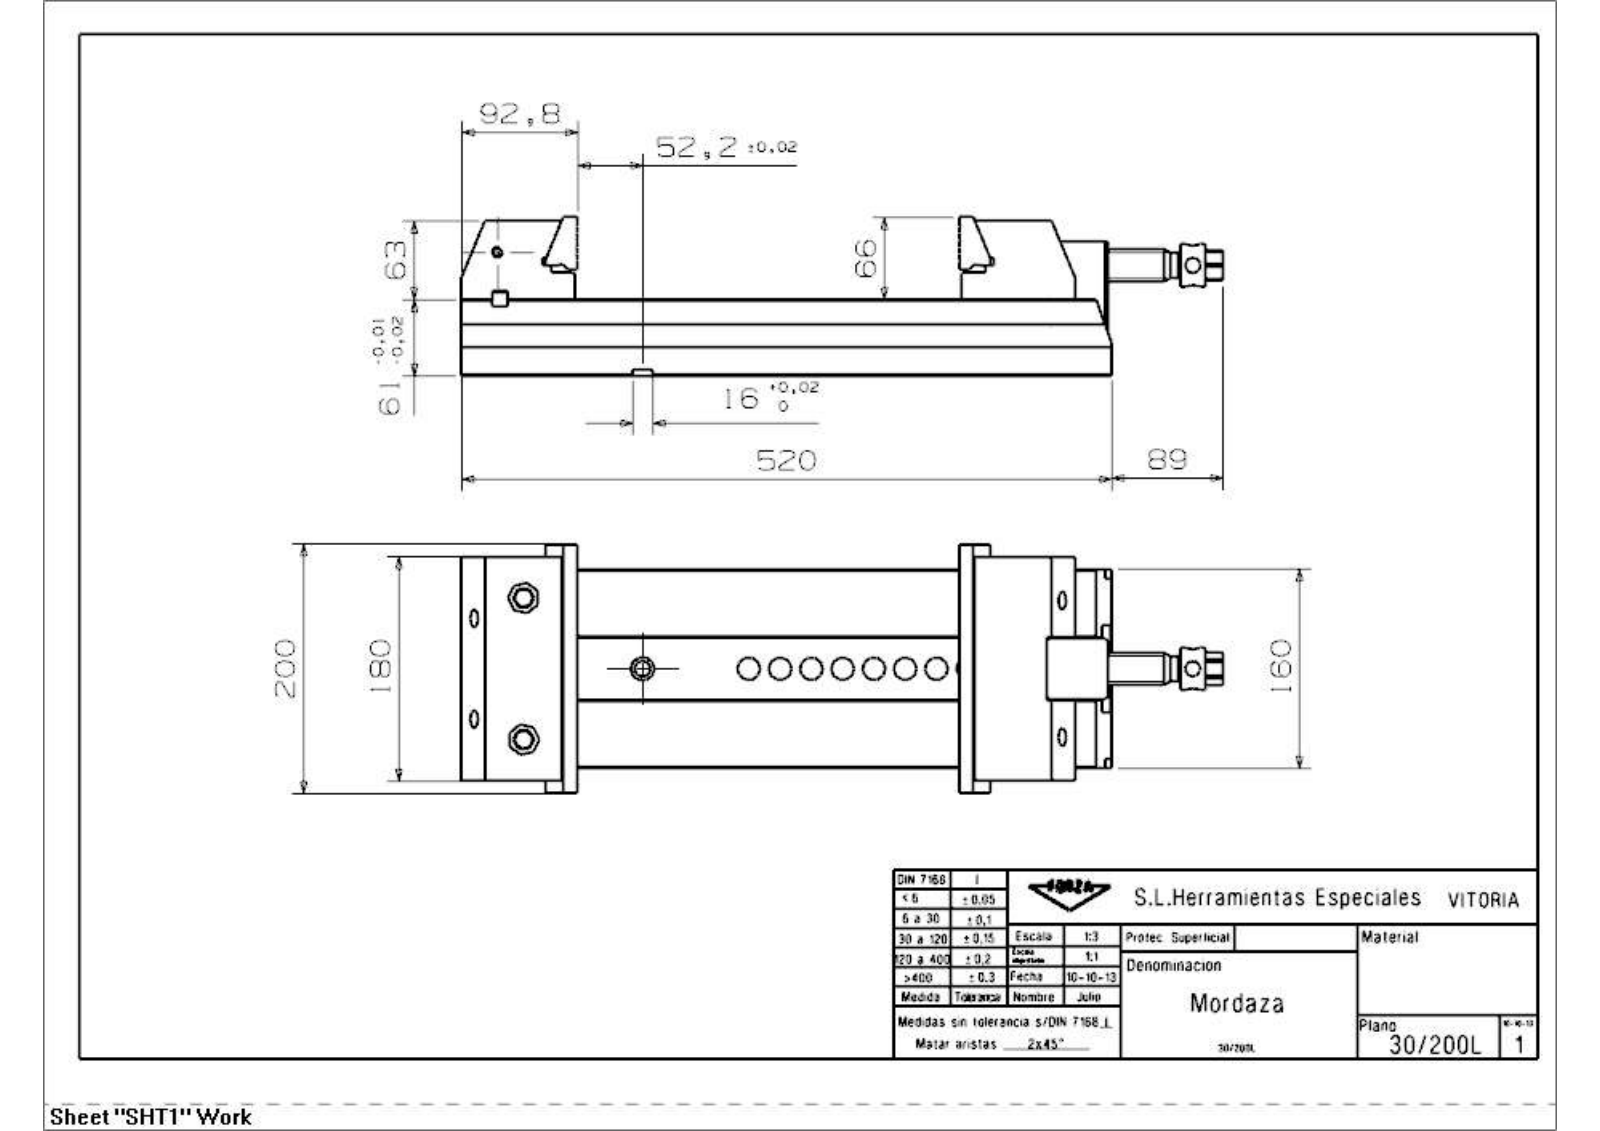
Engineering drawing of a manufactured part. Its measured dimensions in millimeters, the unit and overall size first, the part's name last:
Units: millimetres
Overall size (bounding box): 609 × 200 × 126.95
Round holes (diameter × count): ⌀15 ×6, ⌀5.19 ×5, ⌀13 ×5, ⌀19 ×5, ⌀6.99 ×4, ⌀8.5 ×4, ⌀10 ×4, ⌀8.78 ×3, ⌀10.58 ×3, ⌀12 ×2, ⌀12.38 ×2, ⌀14.38 ×2
Round bosses / shafts (diameter × count): ⌀34 ×1, ⌀33.8 ×1, ⌀26 ×1, ⌀20 ×1, ⌀16.5 ×1
Partial cylindrical surfaces — rounded edges, fillets, slot ends (radius × count): R0.4 ×24, R8 ×4, R20 ×4, R1.6 ×2, R6 ×2, R7 ×2, R4 ×1, R9 ×1
Main face-to-face distances: 61, 29.2, 31.8, 45, 160, 124, 94.8, 63, 10, 1.1
Hole centre spacings: 14.5, 95.5, 81, 110, 293, 16.47, 16.55, 24.08
Volume: 5 906 000 mm³ · Surface area: 621 080 mm²
Bodies: 12 solids, 475 faces (288 planar, 132 cylindrical, 55 other)
Part name (STEP PRODUCT): 30_200L_Mordaza
STEP written by: SIEMENS PLM Software NX 7.5 (CONFIG_CONTROL_DESIGN)
